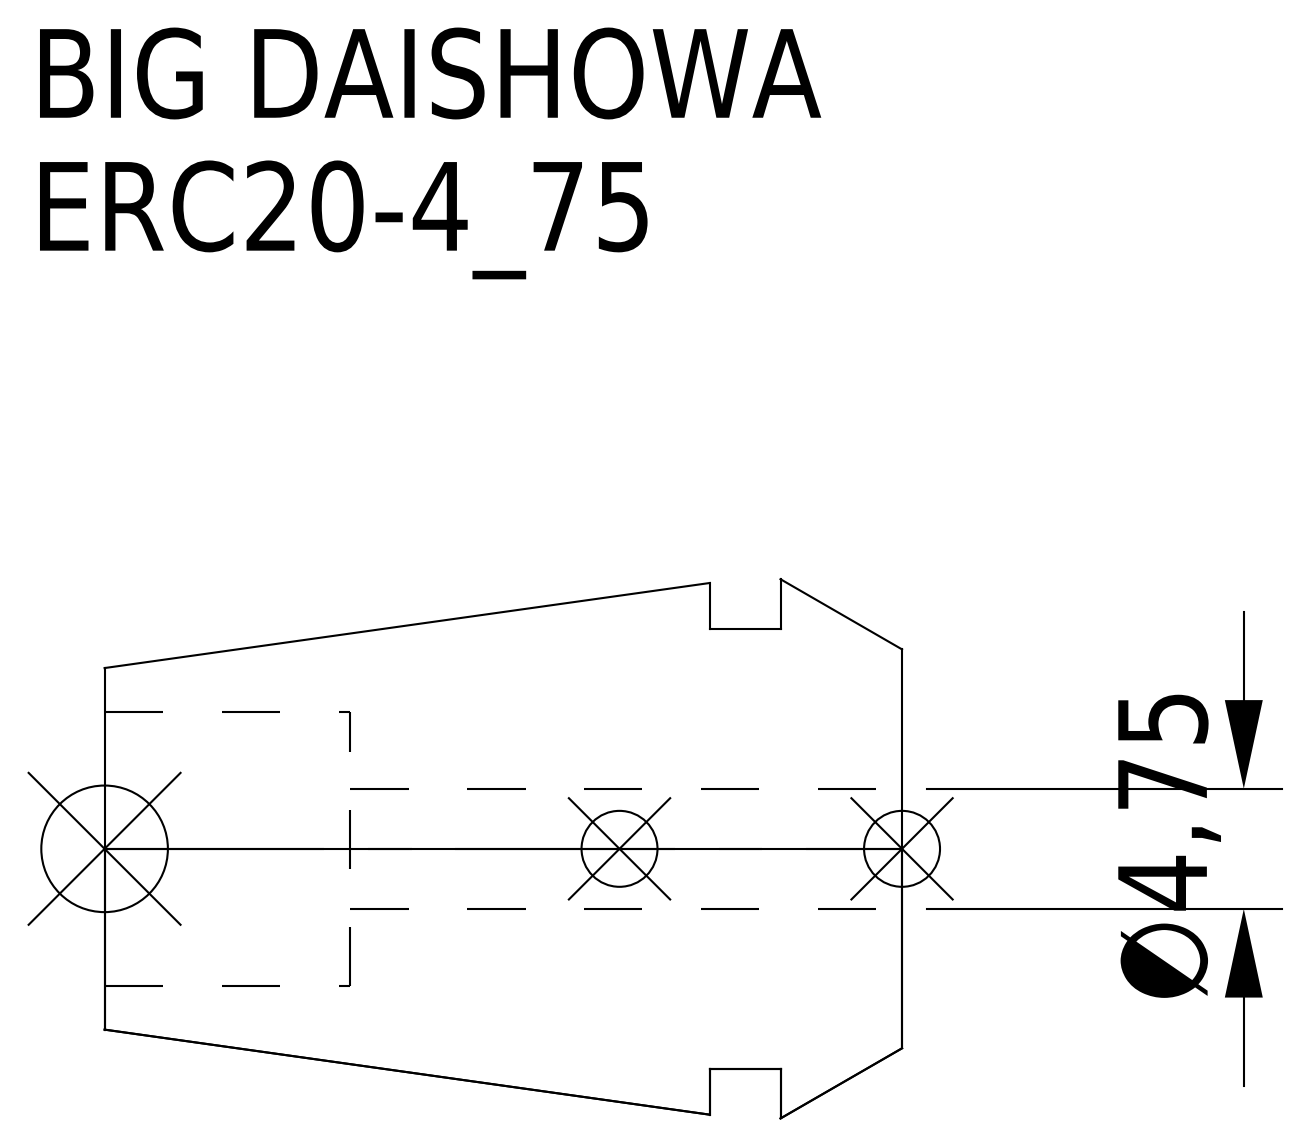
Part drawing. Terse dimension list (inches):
name: ERC20-4_75
written by: CREO PARAMETRIC BY PTC INC, 2016380 (AUTOMOTIVE_DESIGN)
unit: in
bodies: 1 solid, 15 faces (5 planar, 6 cylindrical, 4 other)
size: 1.24 × 0.839 × 0.839
volume: 0.403 in³; area: 4.673 in²
holes: 1× ⌀0.187, 1× ⌀0.425
bosses: 1× ⌀0.685
face distances: 0.189, 0.299, 0.11, 0.858, 0.669, 0.559, 1.24, 1.051, 0.941, 0.382
